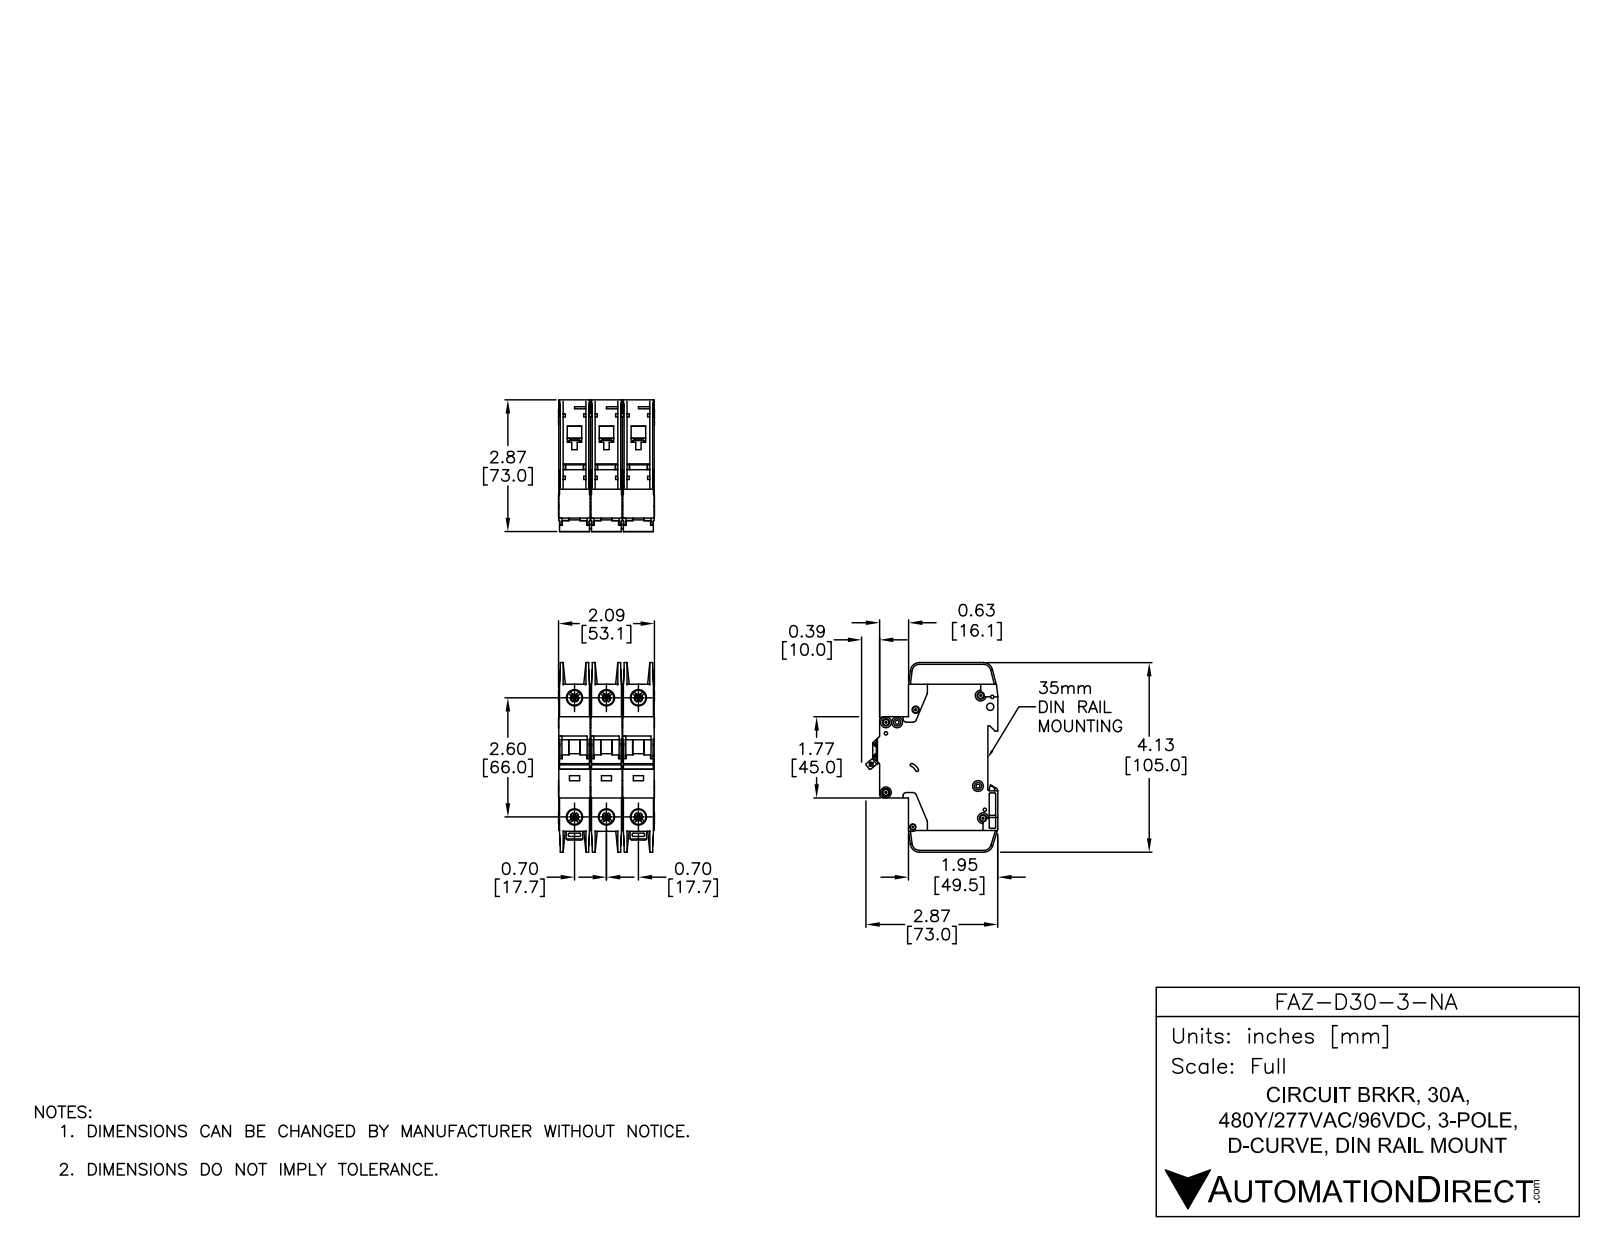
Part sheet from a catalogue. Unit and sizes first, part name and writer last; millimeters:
Units: millimetres
Overall size (bounding box): 105 × 73.04 × 53.1
Round holes (diameter × count): ⌀3.6 ×7, ⌀7.15 ×6, ⌀8.2 ×6, ⌀1.09 ×2, ⌀1.5 ×2, ⌀4 ×2, ⌀1.9 ×1, ⌀2.15 ×1, ⌀2.2 ×1, ⌀2.55 ×1, ⌀3.3 ×1, ⌀3.4 ×1
Round bosses / shafts (diameter × count): ⌀6 ×7, ⌀2.5 ×3
Partial cylindrical surfaces — rounded edges, fillets, slot ends (radius × count): R0.25 ×65, R0.5 ×30, R1 ×26, R2 ×14, R1.8 ×5, R5 ×5, R4 ×4, R0.2 ×2
Main face-to-face distances: 17.7, 35.4, 17.5, 35.2, 0.7, 15.05, 2.45, 1.75, 15.75, 13.3
Hole centre spacings: 17.7, 68.33, 66, 6.2, 35.4, 74.89, 5.19, 6.1
Volume: 233 085 mm³ · Surface area: 74 219 mm²
Bodies: 9 solids, 2352 faces (1227 planar, 789 cylindrical, 336 other)
Part name (STEP PRODUCT): FAZ-D30-3-NA
STEP written by: SolidWorks 2014 (AUTOMOTIVE_DESIGN)
